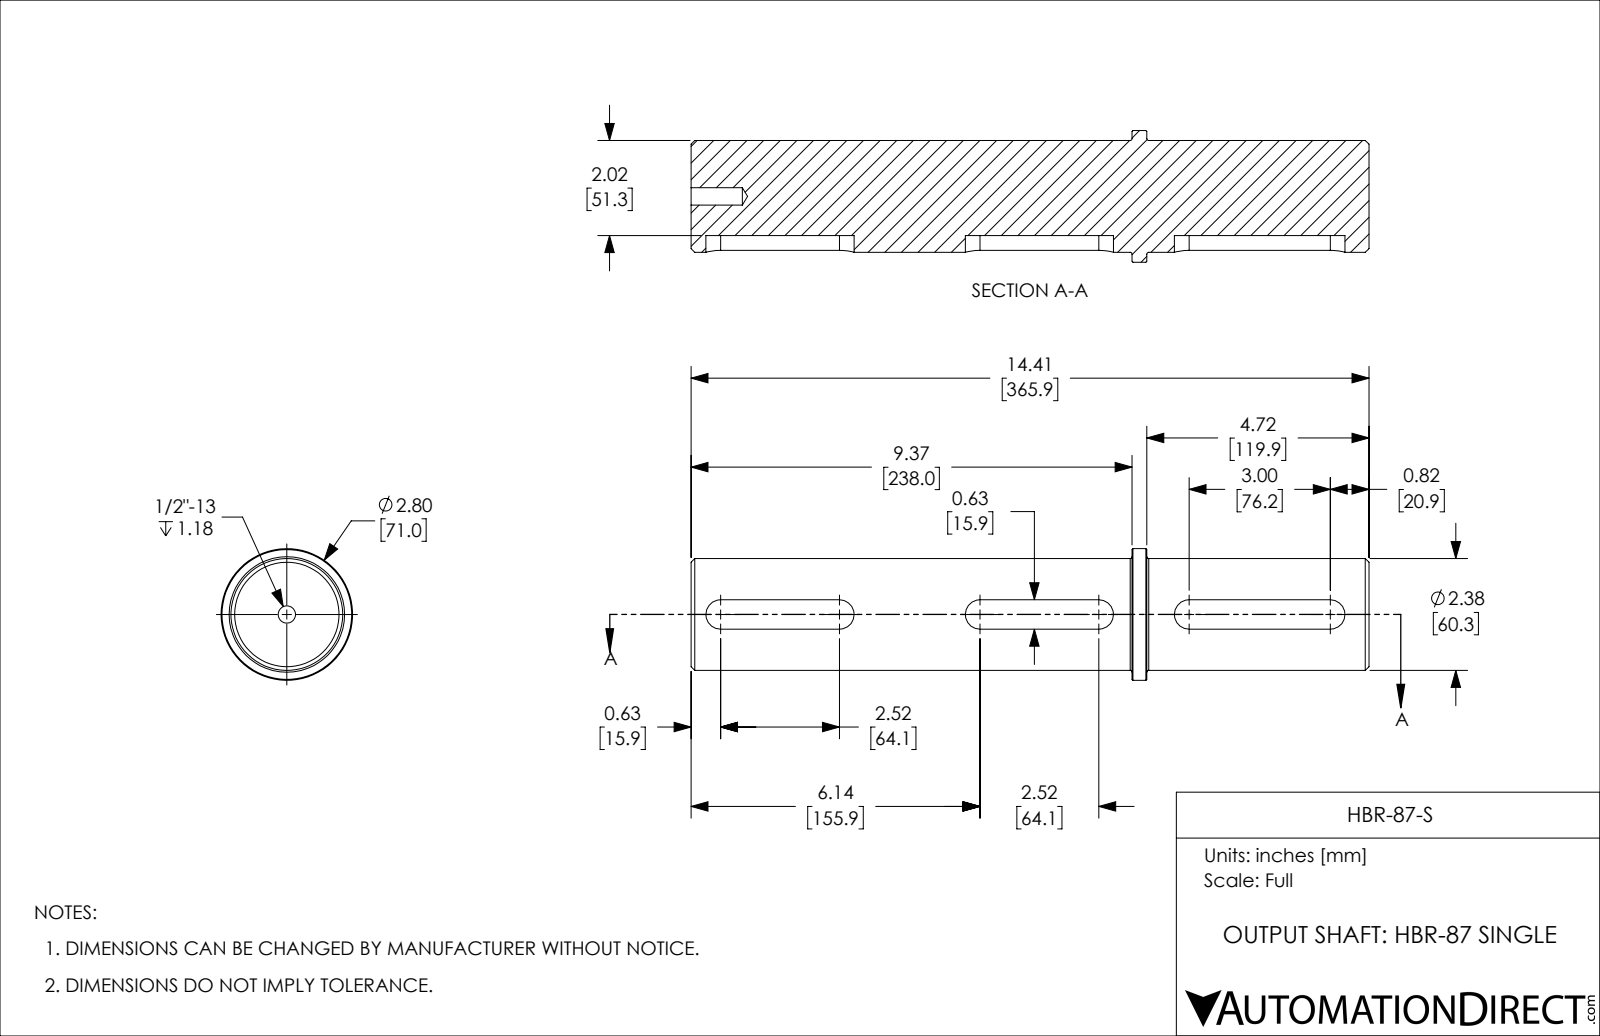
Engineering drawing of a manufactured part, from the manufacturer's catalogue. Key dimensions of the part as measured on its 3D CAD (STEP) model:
Part name (STEP PRODUCT): HBR-87-S
STEP written by: SolidWorks 2018 (AUTOMOTIVE_DESIGN)
Units: inches
Bodies: 1 solid, 44 faces (13 planar, 17 cylindrical, 14 other)
Overall size (bounding box): 14.405 × 2.795 × 2.795
Volume: 62.16 in³ · Surface area: 127.2 in²
Round holes (diameter × count): ⌀0.368 ×1
Round bosses / shafts (diameter × count): ⌀2.795 ×1, ⌀2.375 ×1
Partial cylindrical surfaces — rounded edges, fillets, slot ends (radius × count): R0.312 ×4, R0.313 ×2
Main face-to-face distances: 14.405, 0.625, 9.37, 5.035, 9.685, 0.315, 4.72
